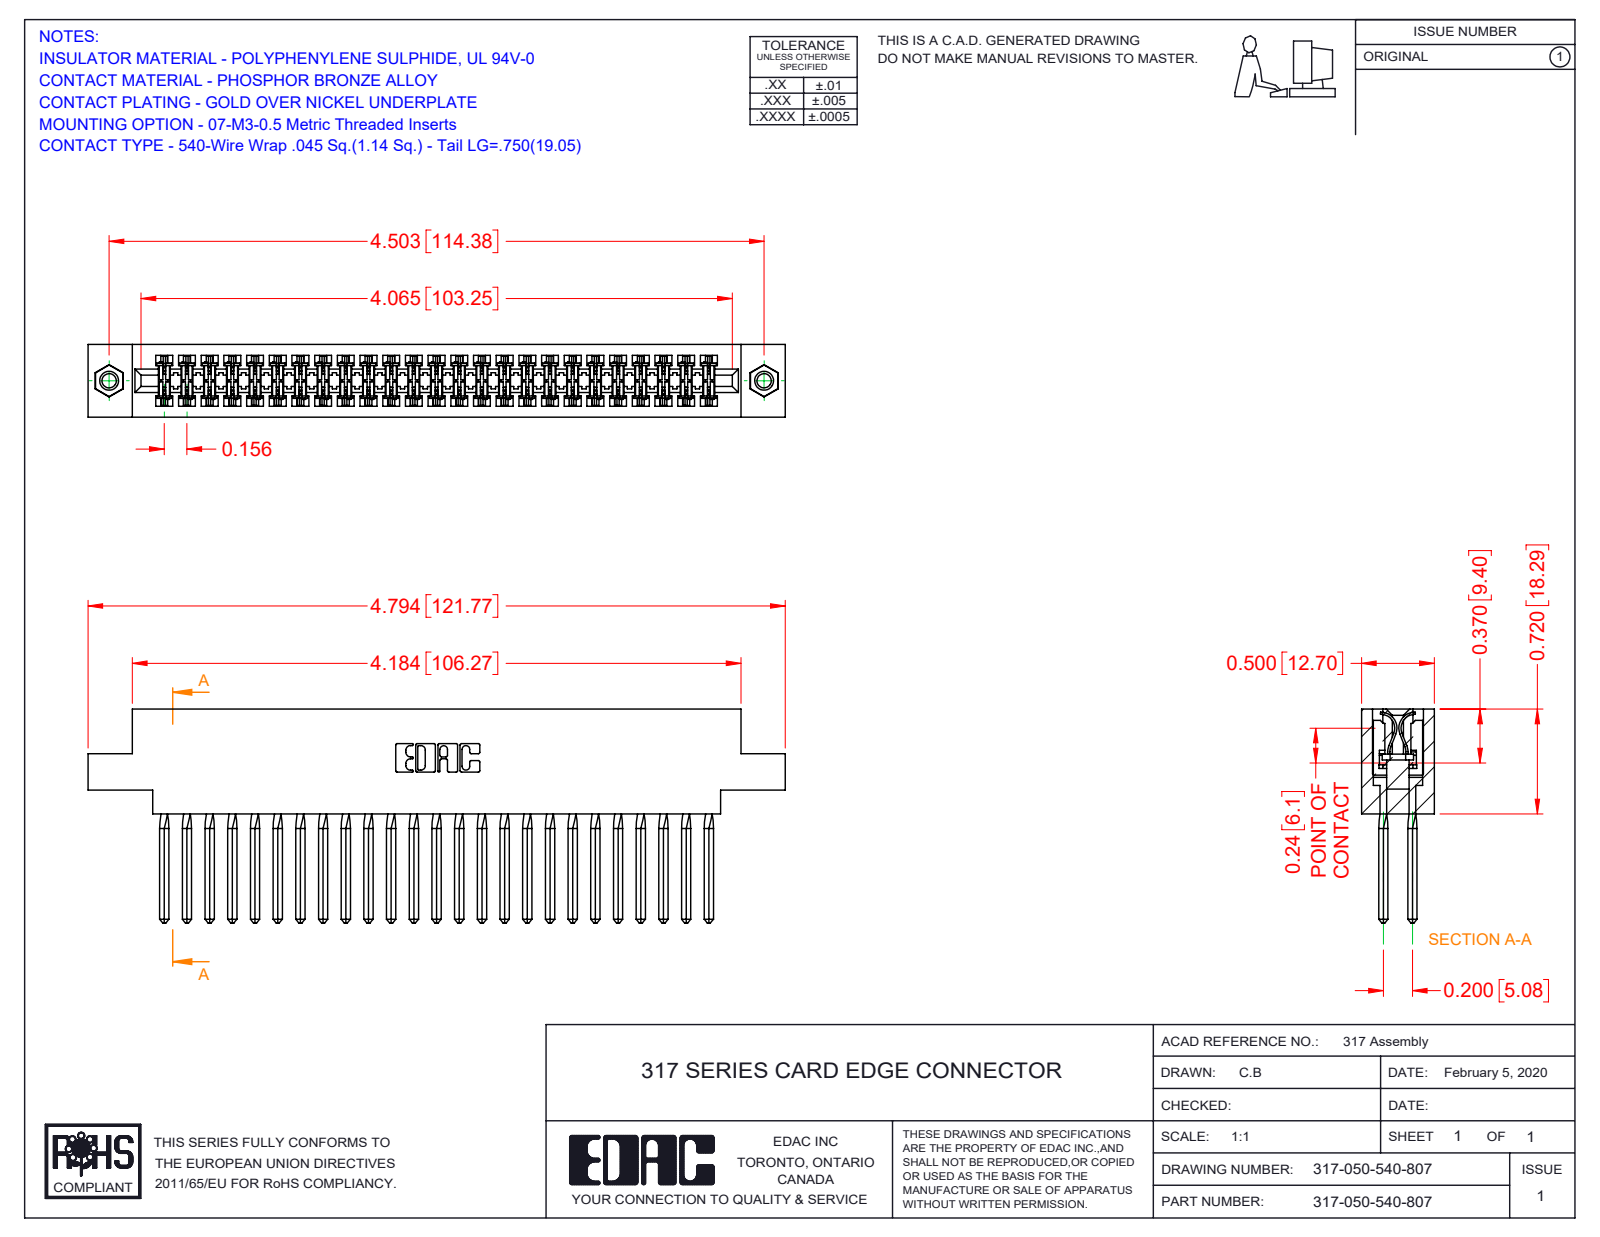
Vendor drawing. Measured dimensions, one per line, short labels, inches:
name: 317-290-001_540; 345-250-001_345-250-005-103; 317-050-540-807; 317 Part_.156 Dia - TI
written by: SolidWorks 2016 (CONFIG_CONTROL_DESIGN)
unit: in
bodies: 53 solids, 4612 faces (3740 planar, 656 cylindrical, 216 other)
size: 4.794 × 1.47 × 0.5
volume: 1.211 in³; area: 44.93 in²
holes: 2× ⌀0.098, 2× ⌀0.125, 2× ⌀0.156
bosses: 2× ⌀0.155
rounds: 100× R0.015, 22× R0.01, 6× R0.007, 6× R0.031, 3× R0.026, 2× R0.095, 2× R0.1, 2× R0.11
face distances: 0.5, 0.075, 0.425, 0.35, 0.11, 0.195, 0.094, 0.72, 0.2, 0.115
hole spacings: 4.503
